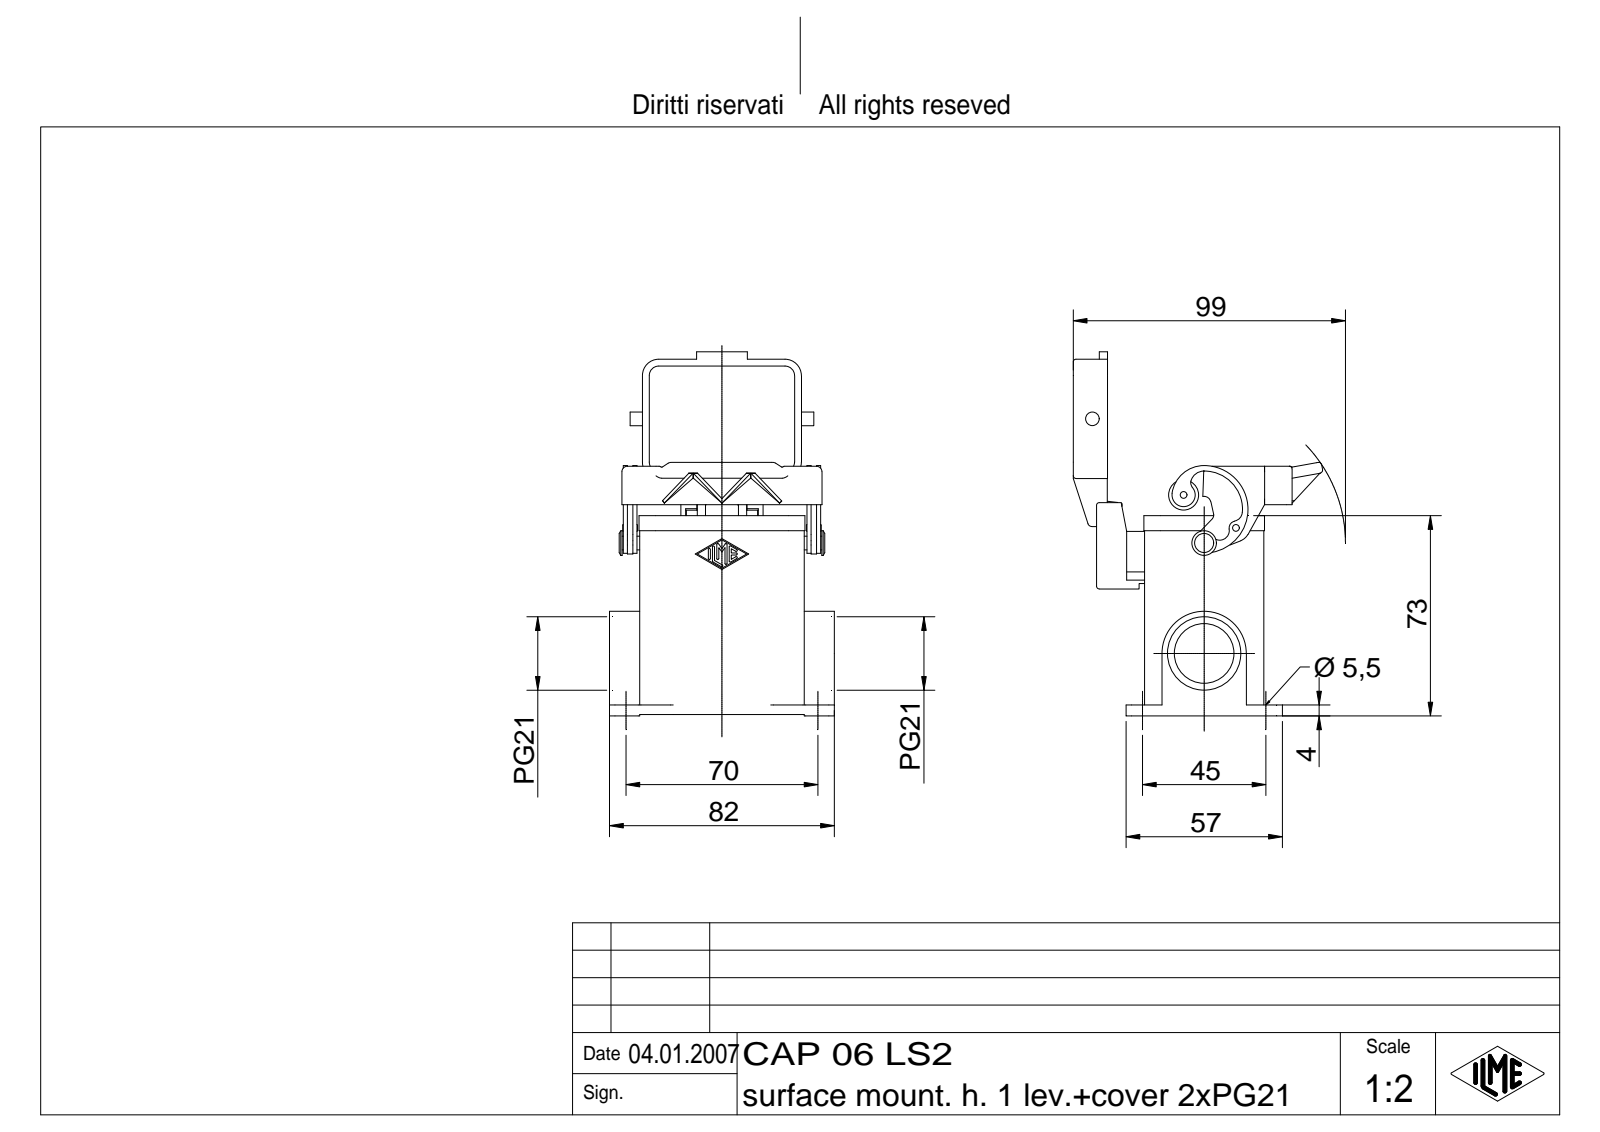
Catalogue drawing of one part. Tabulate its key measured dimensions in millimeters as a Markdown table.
| quantity | value |
| --- | --- |
| part name | CAP 06 LS2 |
| STEP written by | Autodesk Inventor 7 (AUTOMOTIVE_DESIGN) |
| units | millimeters |
| bodies | 2 solids, 695 faces (246 planar, 232 cylindrical, 217 other) |
| overall size | 132.7 × 90.95 × 82 |
| volume | 115 777 mm³ |
| surface area | 61 931 mm² |
| round holes (diameter × count) | 5.5 × 2, 2.5 × 1, 4 × 1, 5 × 1, 21.78 × 1, 26.78 × 1 |
| round bosses / shafts (diameter × count) | 5 × 2, 11 × 1, 9 × 1, 7 × 1, 4 × 1, 3 × 1, 2 × 1 |
| partial cylindrical surfaces (radius × count) | 2 × 28, 1 × 22, 0.38 × 14, 6 × 12, 0.7 × 8, 3.5 × 6, 1.5 × 4, 3 × 4 |
| main face-to-face distances | 3, 40.5, 3.5, 43.5, 4, 26, 37.5, 66.5, 69.5, 29 |
| hole center spacings | 47.2, 83.22 |
